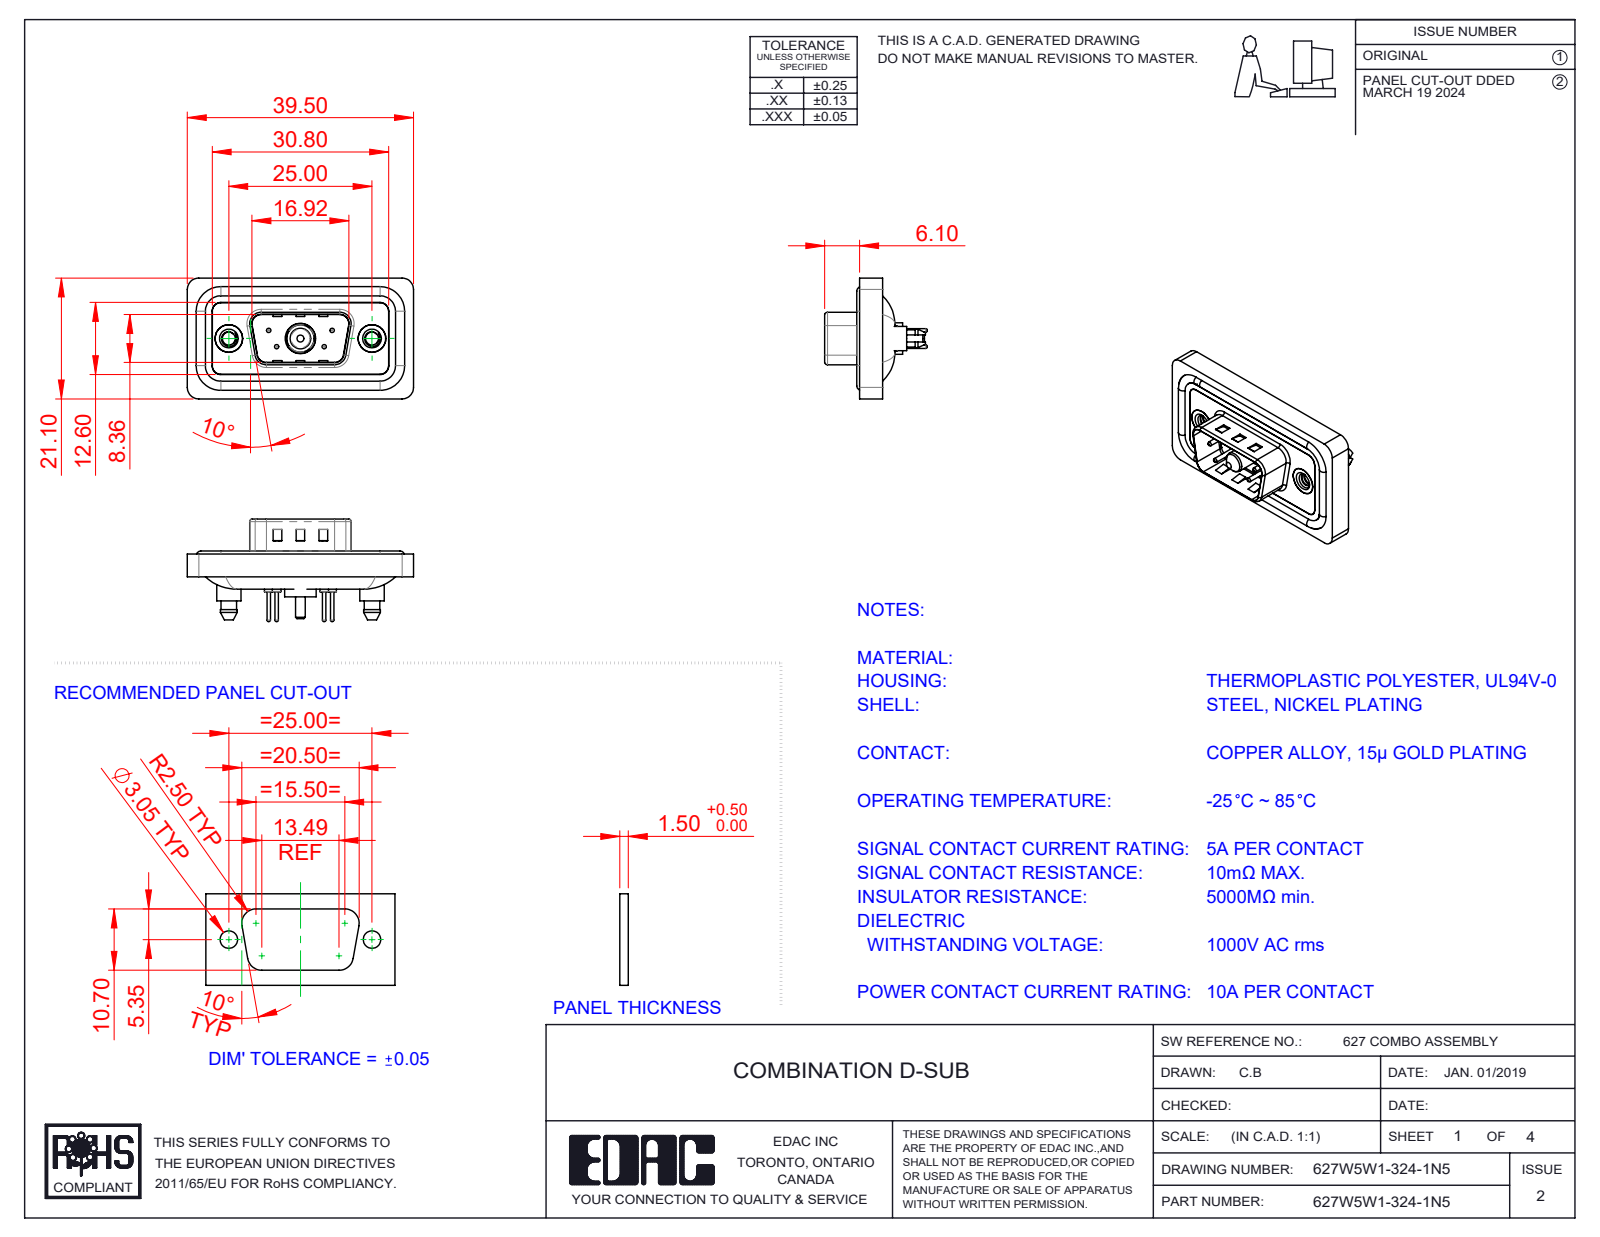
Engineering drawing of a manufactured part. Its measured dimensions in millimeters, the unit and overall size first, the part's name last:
Units: millimetres
Overall size (bounding box): 39.5 × 21.1 × 17.9
Round holes (diameter × count): ⌀0.75 ×4, ⌀1.6 ×4, ⌀2 ×4, ⌀2.26 ×2, ⌀4 ×2, ⌀4.8 ×2, ⌀5 ×2, ⌀4.85 ×1, ⌀5.3 ×1
Round bosses / shafts (diameter × count): ⌀1.6 ×4, ⌀1.5 ×4, ⌀0.6 ×4, ⌀5.4 ×2, ⌀4.9 ×2, ⌀4.25 ×2, ⌀5.5 ×1, ⌀5.2 ×1
Partial cylindrical surfaces — rounded edges, fillets, slot ends (radius × count): R1.5 ×24, R2 ×18, R1.6 ×10, R0.5 ×8, R0.25 ×4, R0.6 ×4, R0.65 ×4, R0.9 ×4
Main face-to-face distances: 0.4, 1.1, 2.9, 1.6, 1.5, 3.1, 0.5, 2.5, 4, 0.7
Hole centre spacings: 3.16, 5.72, 7.1, 12.5, 18.1, 4.39, 4.4, 8.31
Volume: 4 507 mm³ · Surface area: 7 262 mm²
Bodies: 13 solids, 648 faces (199 planar, 287 cylindrical, 162 other)
Part name (STEP PRODUCT): 627Combo Contact Row 1_24; 627Combo Waterproof Housing_09 Contacts; 627Combo Housing_5W1; 627W5W1-324-1N5 (+5 more)
STEP written by: SolidWorks 2023 (CONFIG_CONTROL_DESIGN)
